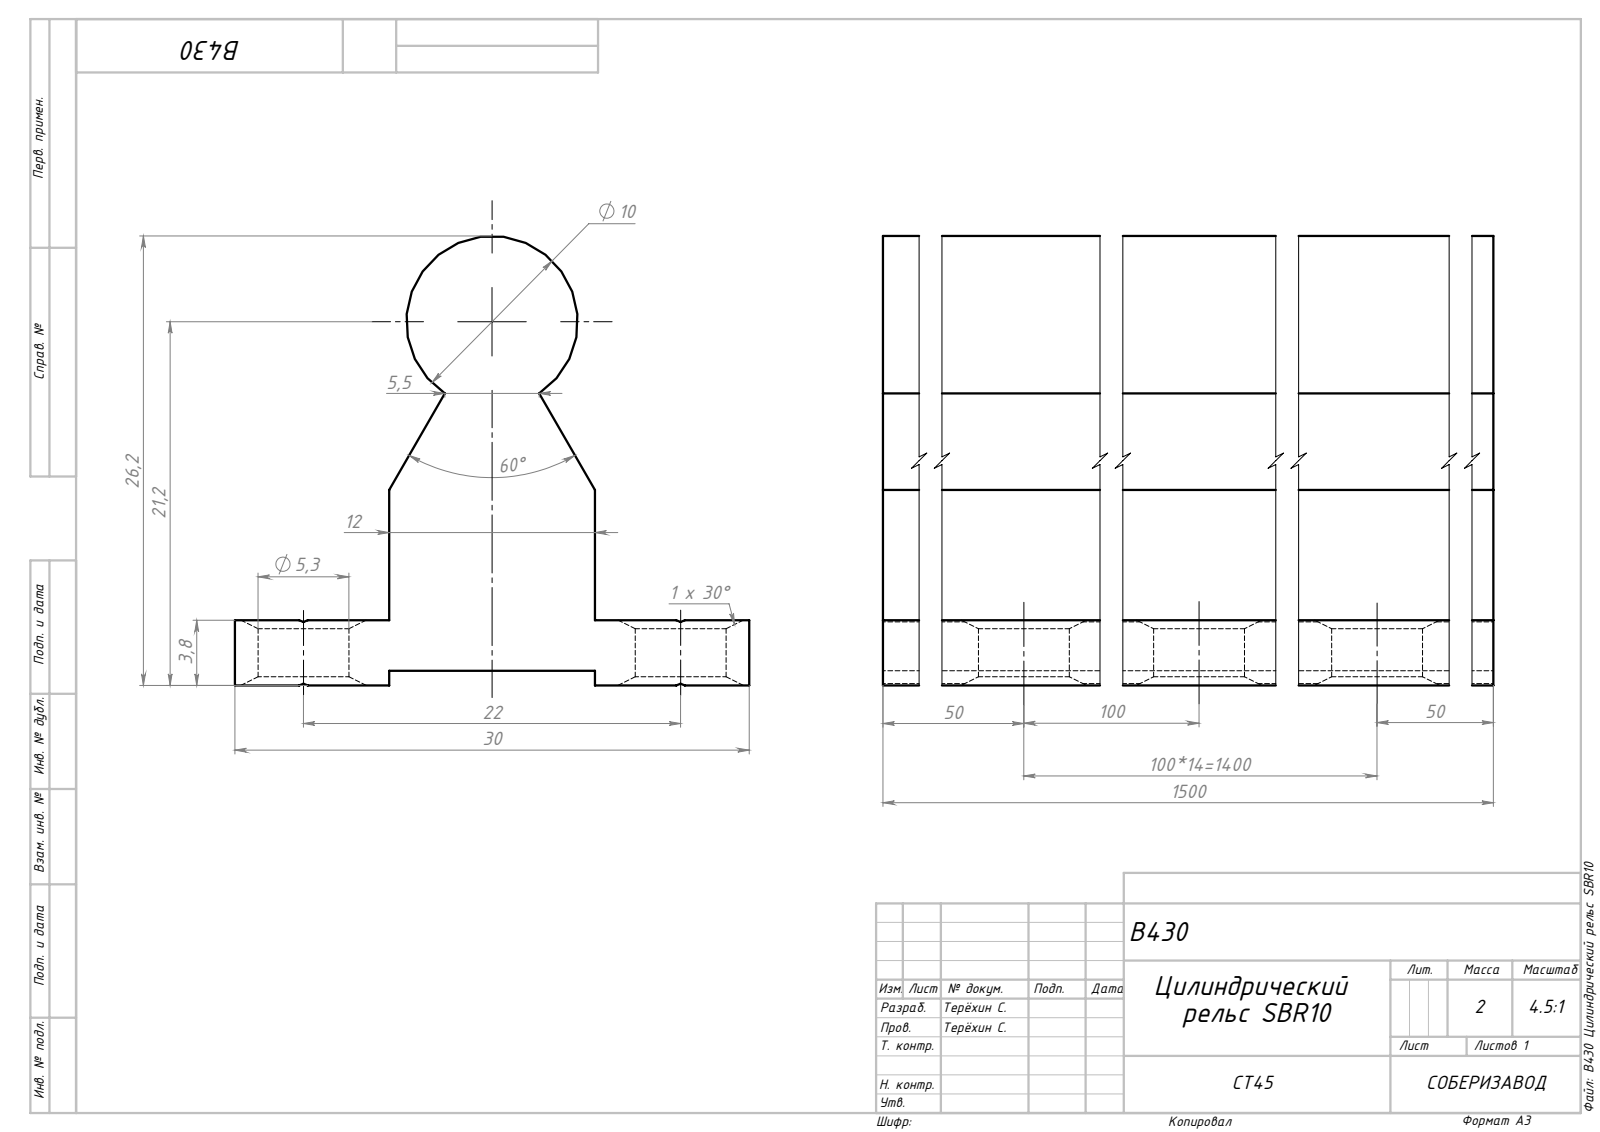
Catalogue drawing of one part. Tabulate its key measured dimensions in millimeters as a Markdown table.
| quantity | value |
| --- | --- |
| part name | B430 Цилиндрический рельс SBR10_00; Сборка1 |
| STEP written by | SolidWorks 2022 (AUTOMOTIVE_DESIGN) |
| units | millimeters |
| bodies | 1 solid, 330 faces (147 planar, 63 cylindrical, 120 other) |
| overall size | 1500 × 30 × 26.2 |
| volume | 476 554 mm³ |
| surface area | 167 692 mm² |
| round holes (diameter × count) | 5.3 × 30 |
| round bosses / shafts (diameter × count) | 10 × 1 |
| main face-to-face distances | 3.8, 0.85, 2.95, 12, 9, 21, 30, 8.16, 3.34, 11.5 |
| hole center spacings | 100, 102.39, 200, 201.21, 300, 300.81, 400, 400.6 |
